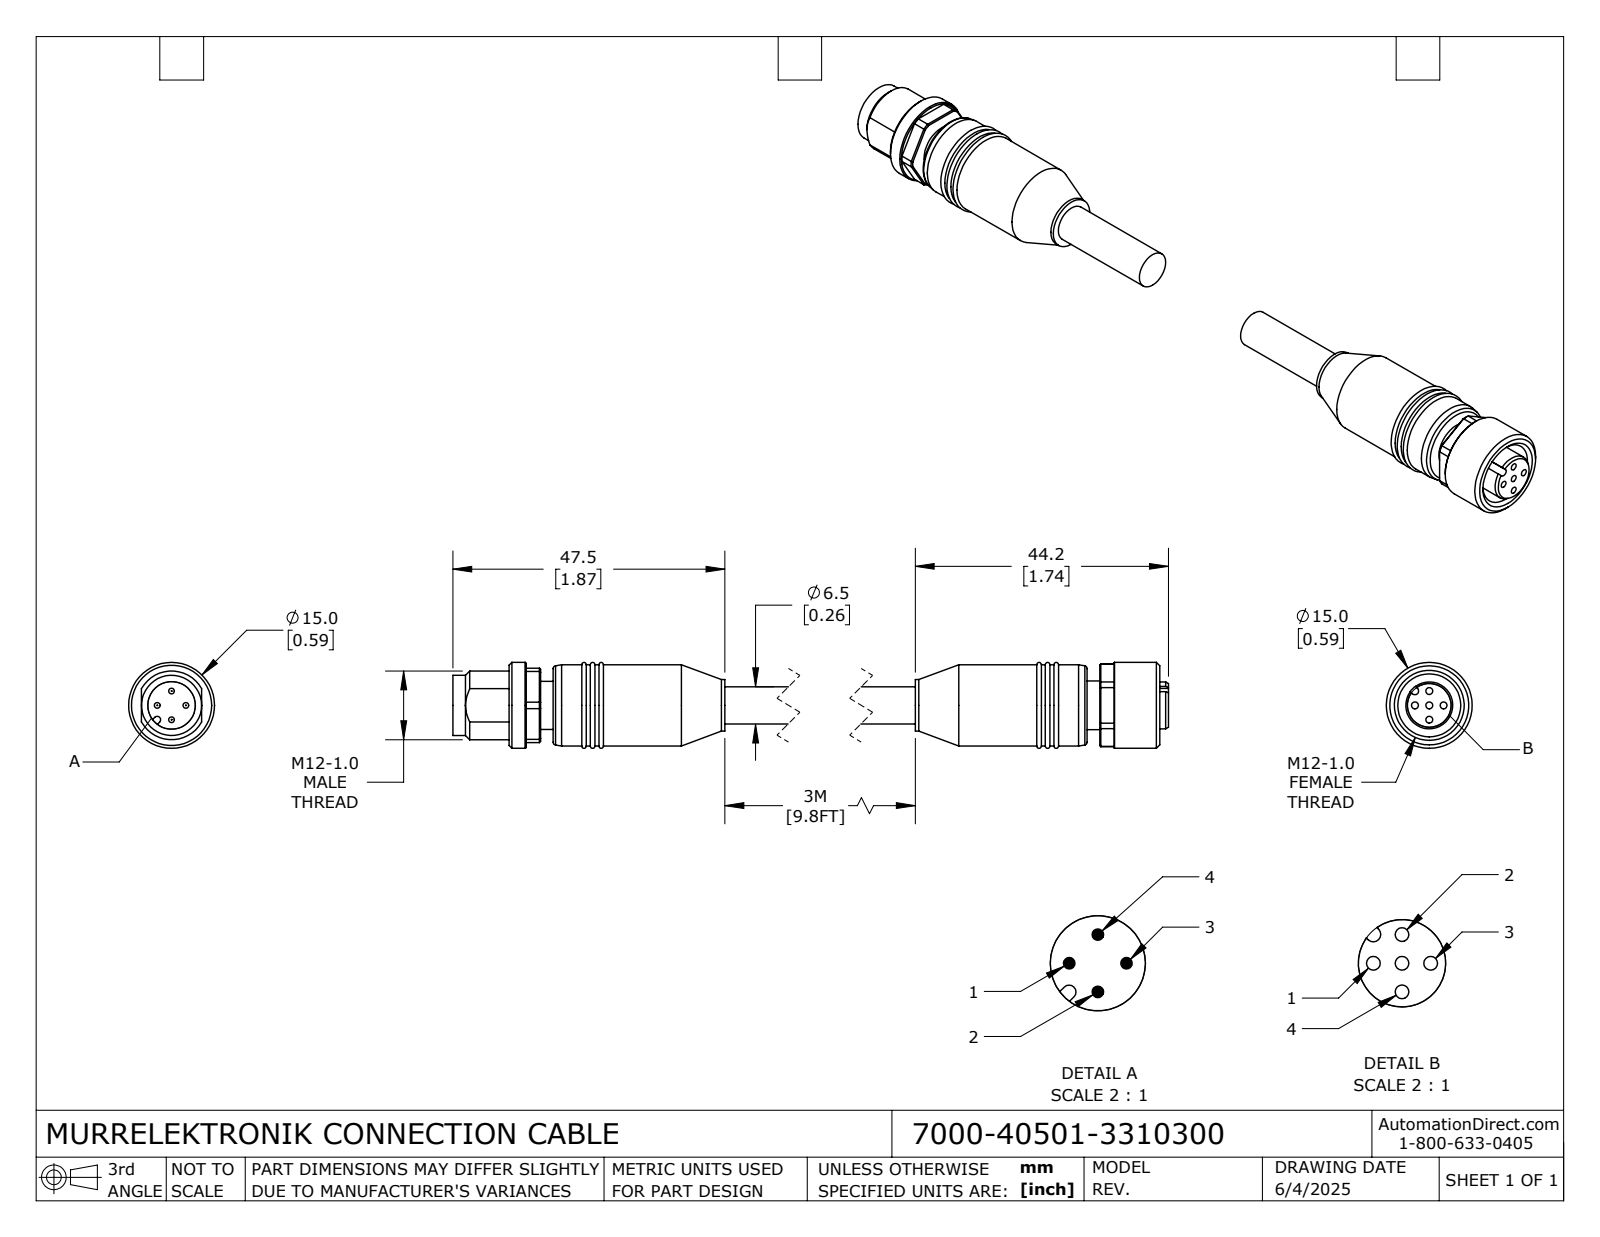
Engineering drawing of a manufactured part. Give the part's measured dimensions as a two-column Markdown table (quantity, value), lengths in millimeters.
| quantity | value |
| --- | --- |
| part name | 7000-40501-3310300; 7000-40501-3310300_MALE; 7000-40501-3310300_FEMALE |
| STEP written by | SolidWorks 2024 (CONFIG_CONTROL_DESIGN) |
| units | millimeters |
| bodies | 2 solids, 193 faces (57 planar, 75 cylindrical, 61 other) |
| overall size | 156.7 × 15 × 15 |
| volume | 13 204 mm³ |
| surface area | 6 518 mm² |
| round holes (diameter × count) | 1.2 × 5, 8.3 × 1, 11 × 1 |
| round bosses / shafts (diameter × count) | 1 × 4, 15 × 1, 14.2 × 1, 10.5 × 1, 9 × 1, 8.5 × 1, 8.4 × 1, 8.2 × 1 |
| partial cylindrical surfaces (radius × count) | 0.6 × 1, 0.65 × 1, 6 × 1, 7.2 × 1 |
| main face-to-face distances | 2.2, 127.2, 13, 129.4, 10.5, 125, 134.9, 52.2, 77.2, 50 |
| hole center spacings | 2.5, 3.54, 5 |
